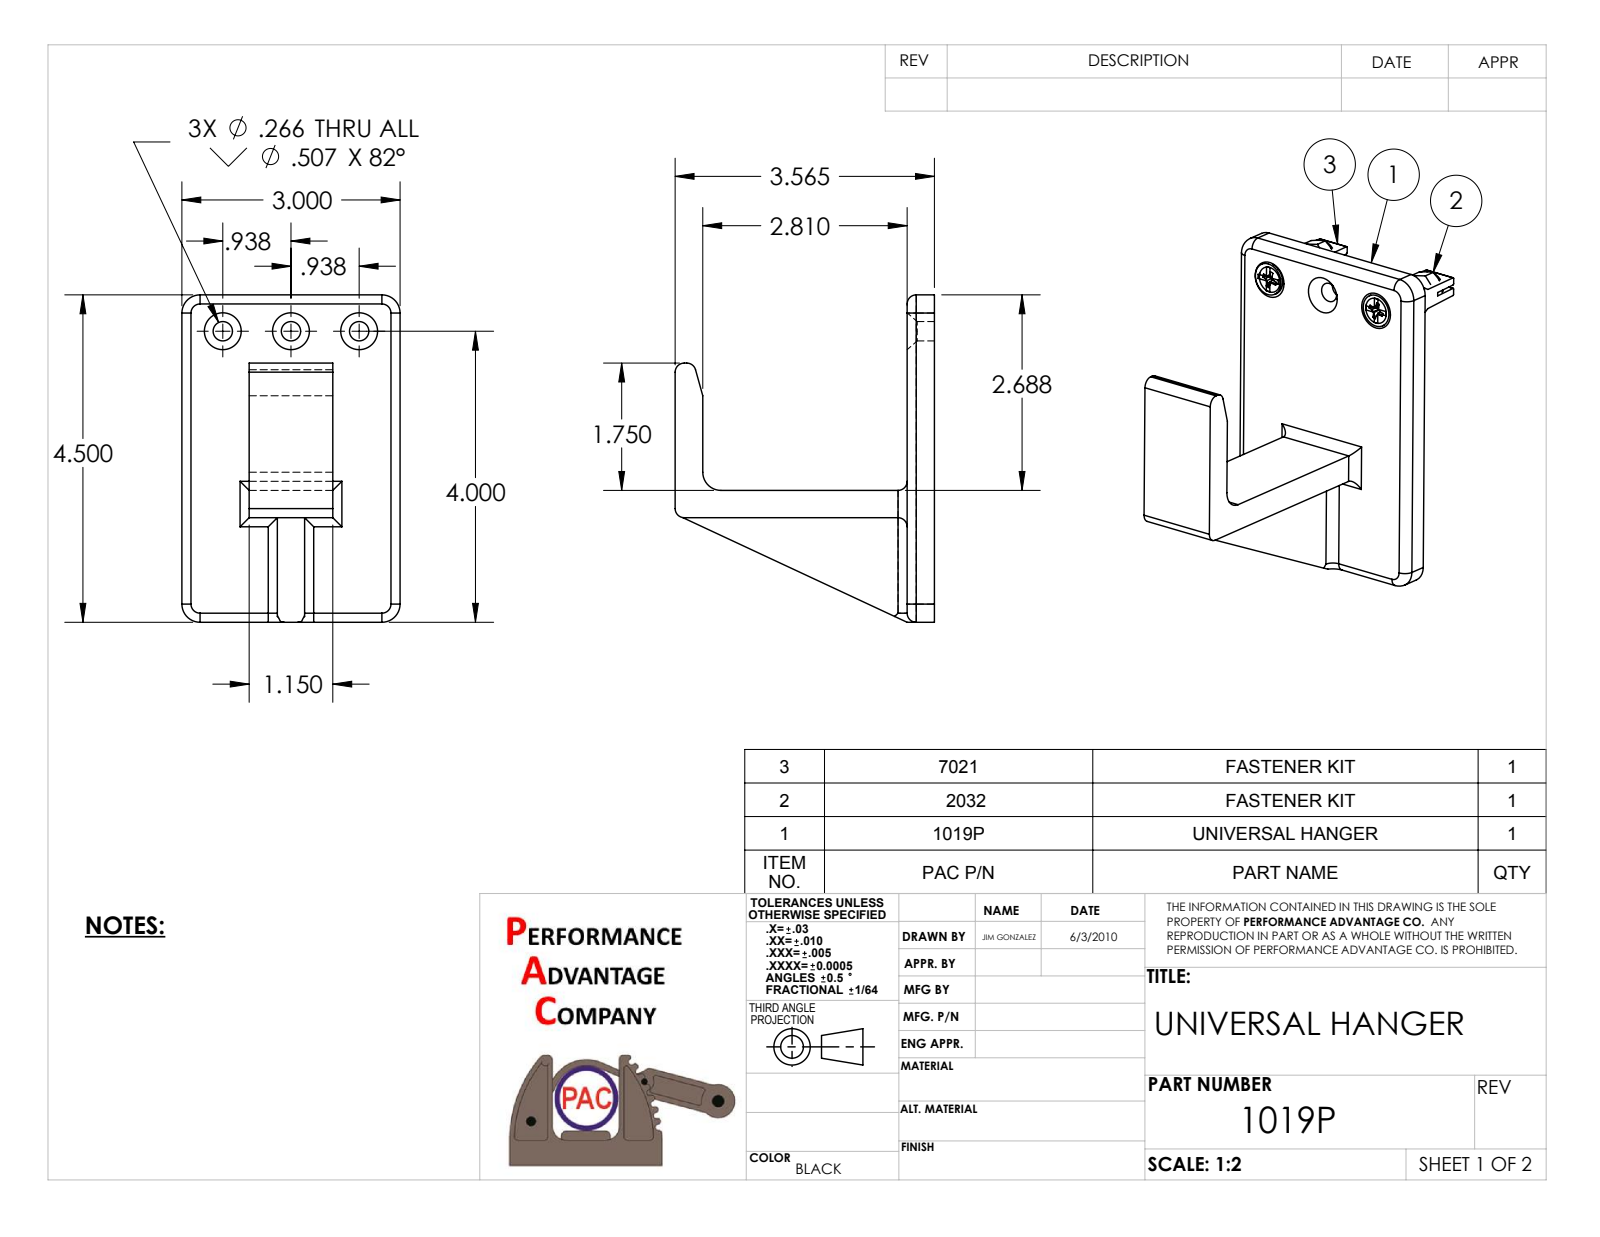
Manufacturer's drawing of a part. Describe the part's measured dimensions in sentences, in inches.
The part is named "1019". Its 3-D file was written by "SolidWorks 2010 (CONFIG_CONTROL_DESIGN)". It is 1 solid with 60 faces: 22 planar, 32 cylindrical and 6 other. Overall it measures 4.5 by 3.565 by 3 inches. Its volume is 7.809 cubic inches and its surface area 51.01 square inches. Round holes: 3 of diameter 0.266, 3 of diameter 0.531. Partial cylindrical surfaces (rounded edges, fillets, slot ends): 13 of radius 0.125, 5 of radius 0.25. The main face-to-face distances are 0.375, 0.375, 0.387, 0.762, 3.565, 3.19, 0.925, 1.313, 1.687, 2.075. The hole center spacings are 0.937, 1.875.
